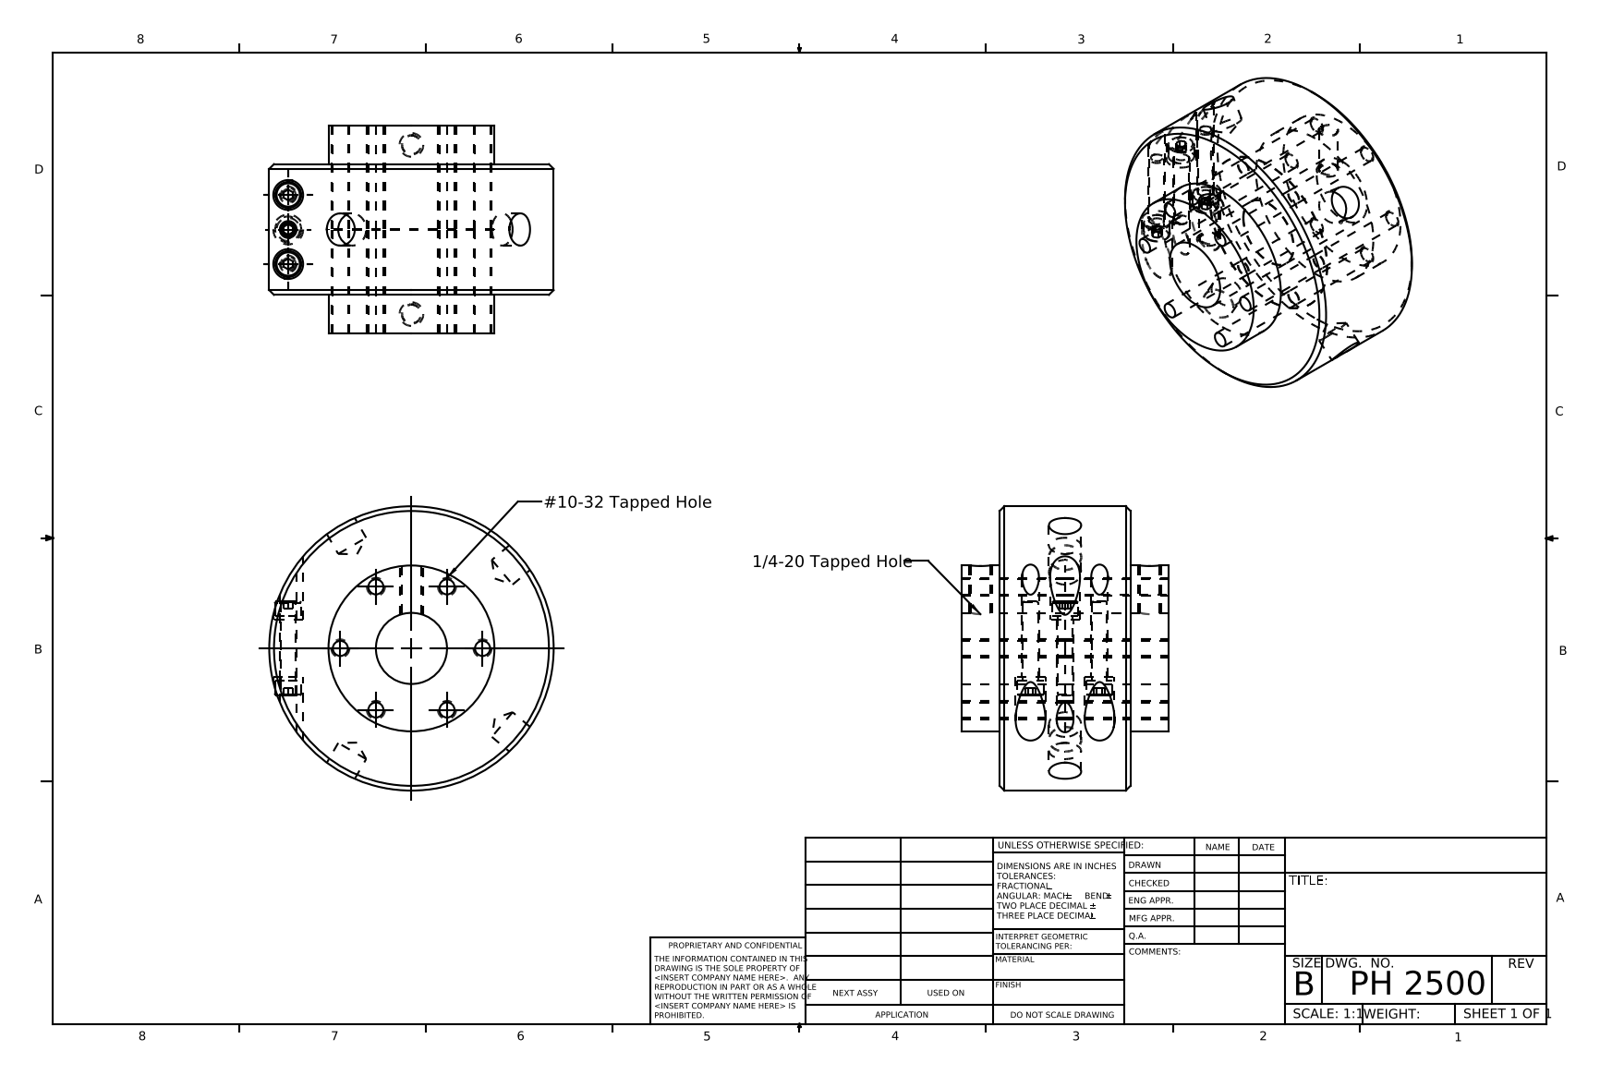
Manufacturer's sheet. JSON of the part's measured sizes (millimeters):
{"part_name": "PH 2500", "step_written_by": "SolidWorks 2010 (CONFIG_CONTROL_DESIGN)", "units": "millimeters", "bodies": {"solids": 4, "faces": 135, "planar": 39, "cylindrical": 72, "other": 24}, "overall_size": [76.2, 76.2, 55.6], "volume_mm3": 167300, "surface_area_mm2": 33190, "round_holes": [[4, 6], [8.6, 4], [4.5, 3], [8, 3], [5.1, 2], [19.1, 1]], "round_bosses_or_shafts": [[7, 3], [4, 3], [76.2, 1], [44.5, 1]], "face_to_face_distances": [35.1, 17.5, 17.6, 10.3, 27.8, 27.9, 45.3, 55.6, 1, 4], "hole_center_spacings": [19.1, 33, 9.2, 19.1, 35.6, 38.1, 40.1, 45.9]}
